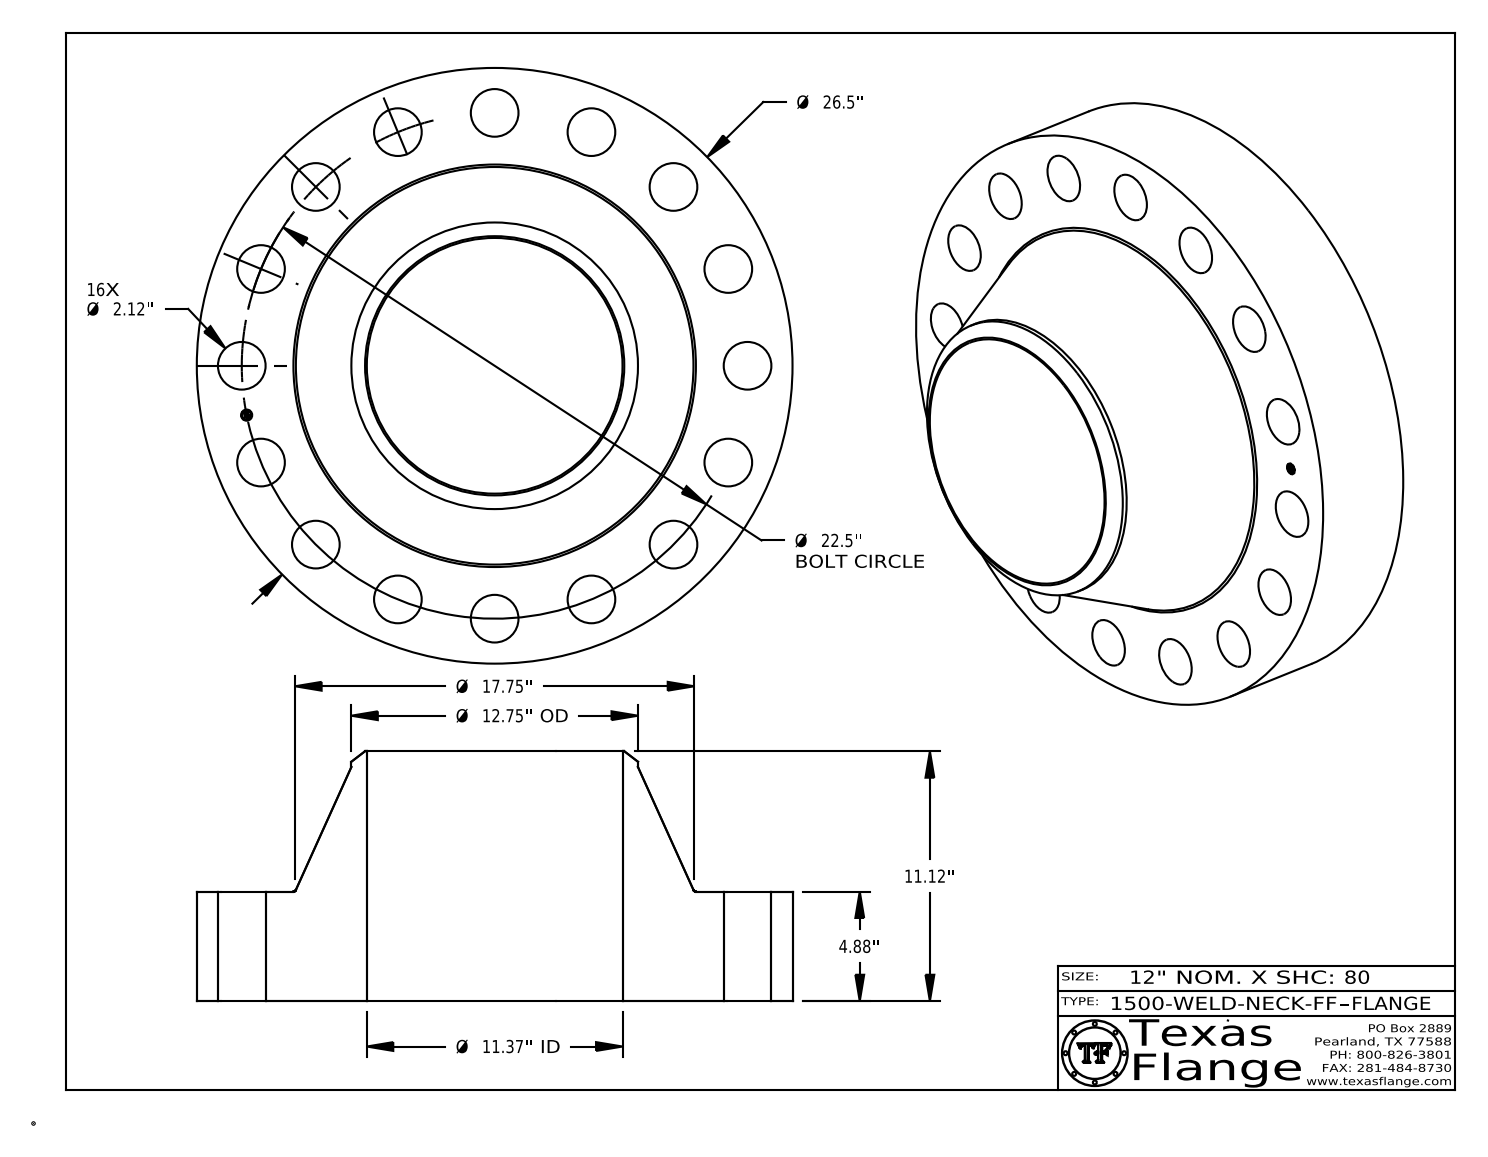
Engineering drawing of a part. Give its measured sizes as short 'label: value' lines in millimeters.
name: 1500-WELD-NECK-FF
written by: CATIA V5 STEP AP214 (AUTOMOTIVE_DESIGN)
unit: mm
bodies: 1 solid, 432 faces (368 planar, 58 cylindrical, 6 other)
size: 673.1 × 673.1 × 282.4
volume: 39 180 000 mm³; area: 1 481 000 mm²
holes: 16× ⌀53.8, 1× ⌀12.6, 1× ⌀288.9
bosses: 8× ⌀0.8, 1× ⌀673.1, 1× ⌀323.9, 1× ⌀9.9
face distances: 124, 282.4, 158.5, 123.6, 0.4, 158.9, 3.8, 3.7, 0.7, 2.4
hole spacings: 317.5, 528, 560.5, 285.8, 218.7, 404.1, 111.5, 111.5
